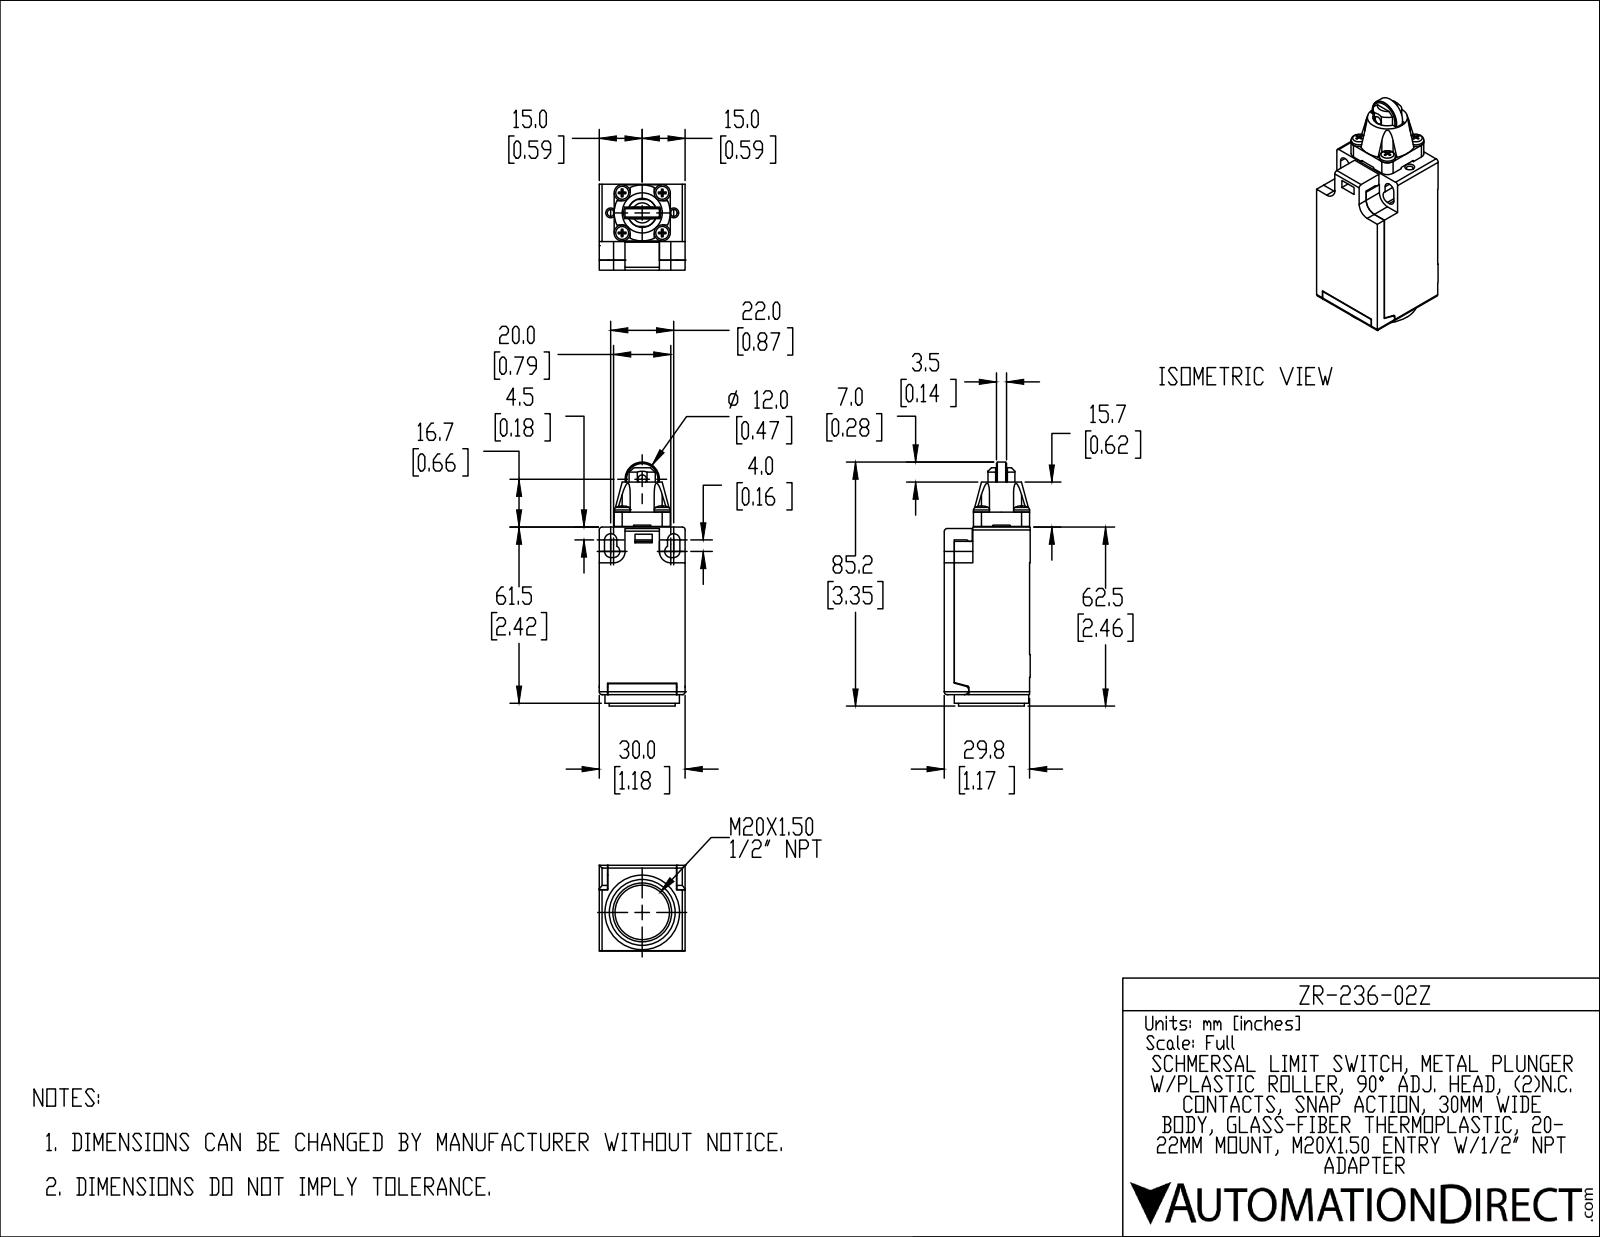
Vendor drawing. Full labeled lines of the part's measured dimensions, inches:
Part name (STEP PRODUCT): ZR-236-02Z
STEP written by: SolidWorks 2019 (AUTOMOTIVE_DESIGN)
Units: inches
Bodies: 3 solids, 322 faces (230 planar, 72 cylindrical, 20 other)
Overall size (bounding box): 3.354 × 1.181 × 1.181
Volume: 3.129 in³ · Surface area: 27.03 in²
Round holes (diameter × count): ⌀0.094 ×6, ⌀0.126 ×4, ⌀0.118 ×1, ⌀0.512 ×1, ⌀0.545 ×1, ⌀0.748 ×1
Round bosses / shafts (diameter × count): ⌀0.213 ×4, ⌀0.221 ×2, ⌀1.024 ×1, ⌀0.906 ×1, ⌀0.472 ×1, ⌀0.415 ×1, ⌀0.276 ×1, ⌀0.248 ×1
Partial cylindrical surfaces — rounded edges, fillets, slot ends (radius × count): R0.11 ×8, R0.039 ×6, R0.085 ×6, R0.11 ×2, R0.157 ×2, R0.024 ×1, R0.059 ×1, R0.197 ×1
Main face-to-face distances: 1.181, 0.138, 1.035, 1.173, 1.043, 0.157, 2.067, 0.118, 0.236, 0.394
Hole centre spacings: 0.317, 0.39, 0.551, 0.76, 0.308, 0.433, 0.454, 0.497
